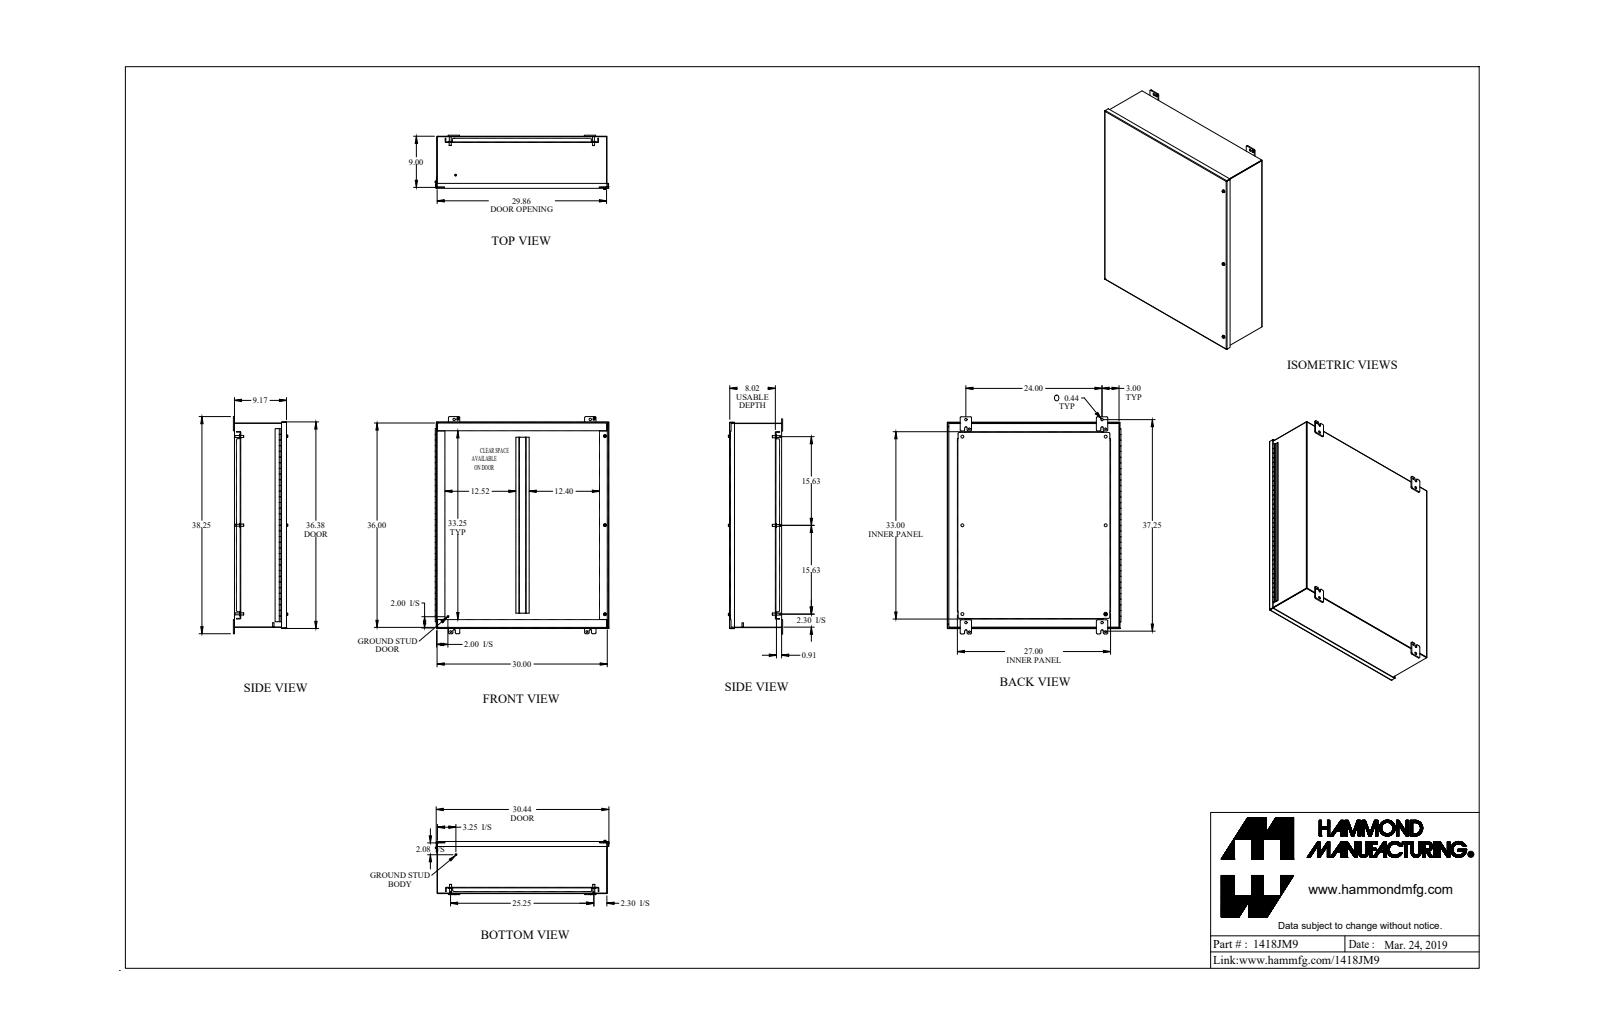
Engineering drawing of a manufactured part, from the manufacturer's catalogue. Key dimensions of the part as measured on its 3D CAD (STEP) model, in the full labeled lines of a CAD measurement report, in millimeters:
Part name (STEP PRODUCT): 1418JM9_Default
STEP written by: SolidWorks 2018 (CONFIG_CONTROL_DESIGN)
Units: millimetres
Bodies: 48 solids, 1273 faces (752 planar, 459 cylindrical, 62 other)
Overall size (bounding box): 971.6 × 777.3 × 243.1
Volume: 6 845 000 mm³ · Surface area: 6 772 000 mm²
Round holes (diameter × count): ⌀8 ×7, ⌀12.7 ×6, ⌀7.8 ×4, ⌀11.1 ×4, ⌀11.3 ×4, ⌀6.6 ×3, ⌀6.8 ×3, ⌀7.1 ×3, ⌀7.4 ×3, ⌀10.1 ×3, ⌀4.7 ×1, ⌀88.9 ×1
Round bosses / shafts (diameter × count): ⌀16.5 ×6, ⌀9.5 ×6, ⌀8.4 ×6, ⌀25.4 ×4, ⌀13 ×3, ⌀12.7 ×3, ⌀9.9 ×3, ⌀6.2 ×3
Partial cylindrical surfaces — rounded edges, fillets, slot ends (radius × count): R4.8 ×37, R6.4 ×28, R2.9 ×16, R0.9 ×10, R2.7 ×10, R5.5 ×8, R3.2 ×7, R3.4 ×6
Main face-to-face distances: 1.8, 231.1, 229.3, 233, 2.4, 28, 26.2, 203.1, 204.9, 25.6
Hole centre spacings: 793.8, 44.1, 398.4, 398.5, 609.6, 908.1, 1093.7, 1.5
